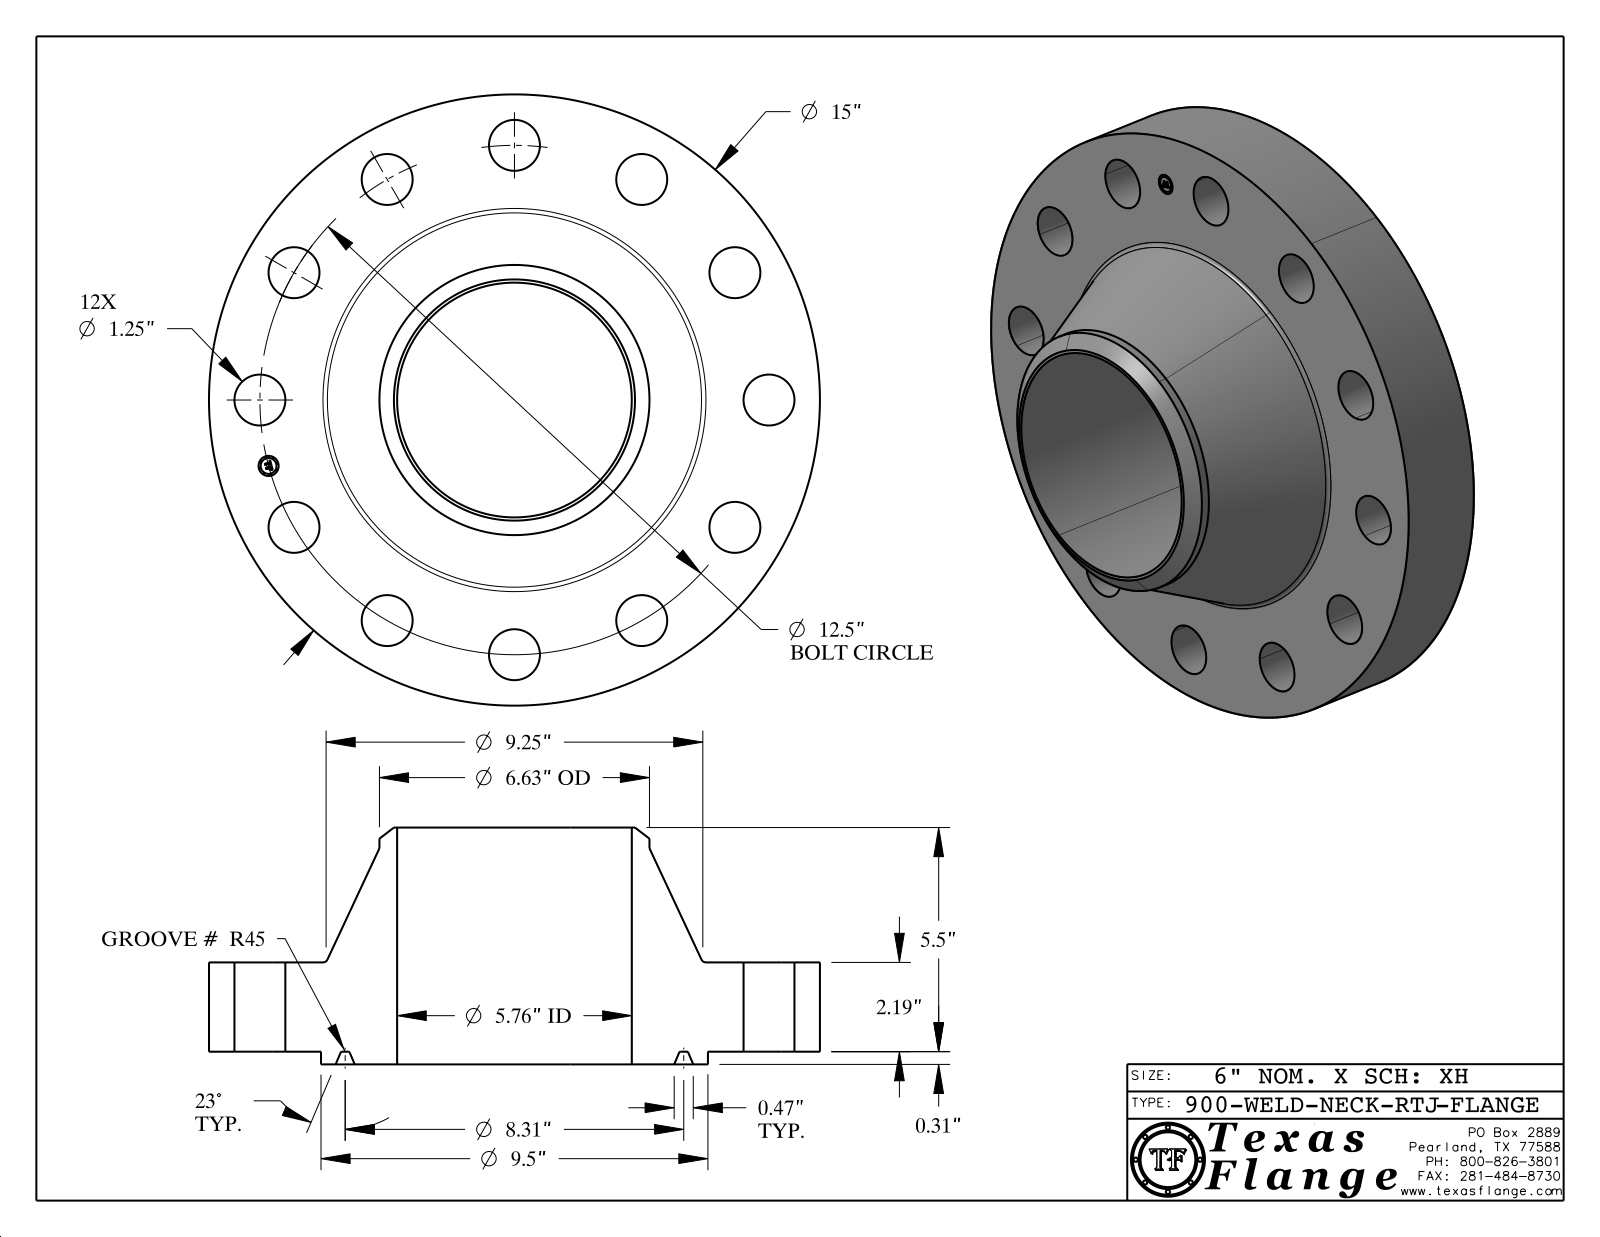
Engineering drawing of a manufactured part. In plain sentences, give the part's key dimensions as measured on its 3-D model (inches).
The part is named "900-WELD-NECK-RTJ". Its 3-D file was written by "CATIA V5 STEP AP214 (AUTOMOTIVE_DESIGN)". It is 1 solid with 437 faces: 371 planar, 52 cylindrical and 14 other. Overall it measures 15 by 15 by 5.813 inches. Its volume is 379.2 cubic inches and its surface area 654.1 square inches. Round holes: 12 of diameter 1.25, 1 of diameter 0.495, 1 of diameter 5.761. Round bosses or shafts: 8 of diameter 0.03, 1 of diameter 15, 1 of diameter 9.5, 1 of diameter 6.63, 1 of diameter 0.39. The main face-to-face distances are 2.19, 0.313, 2.503, 5.813, 5.5, 3.31, 2.488, 2.175, 0.015, 3.325. The hole center spacings are 6.25, 8.839, 3.235, 10.826, 12.074, 12.5, 3.235, 6.25.
